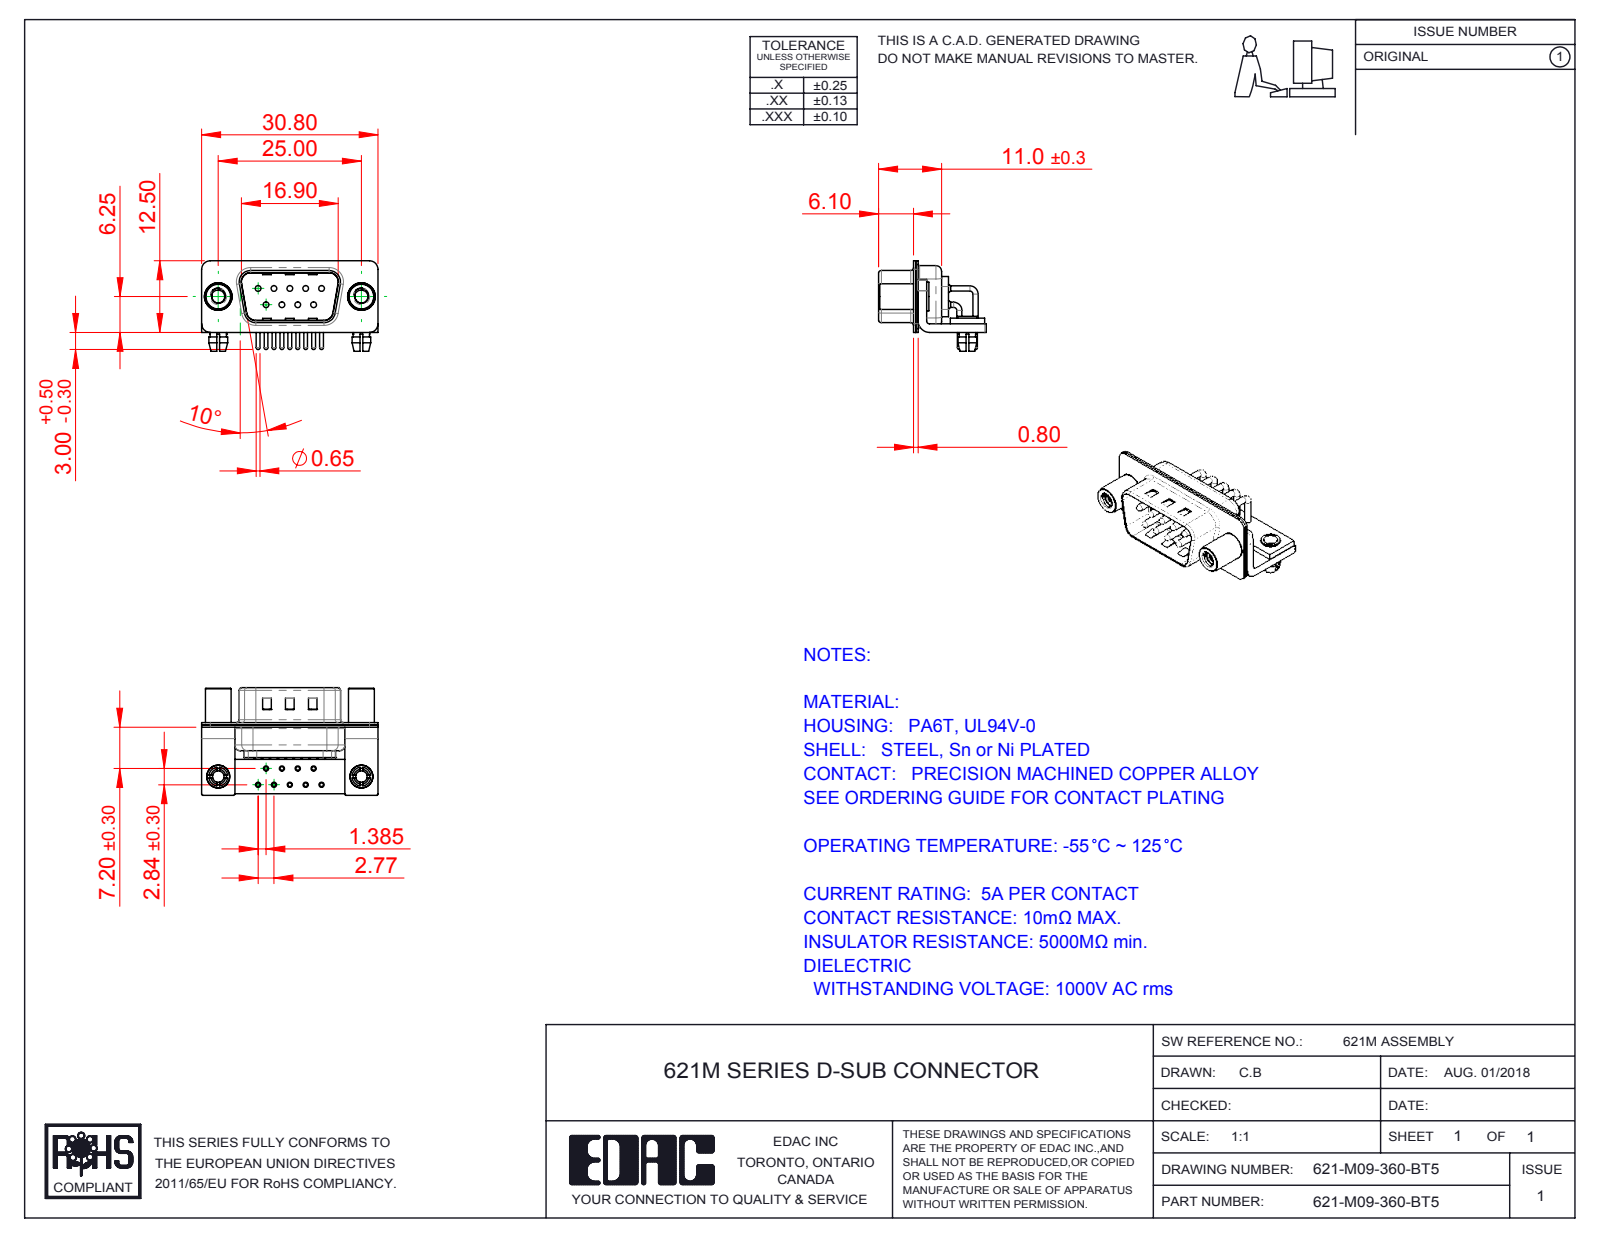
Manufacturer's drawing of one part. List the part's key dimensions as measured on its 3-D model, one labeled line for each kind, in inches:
Part name (STEP PRODUCT): 621-M09-360-BT5; 621M Contact Row 2; 621M Contact Row 1; 621M Board Lock (+6 more)
STEP written by: SolidWorks 2016 (CONFIG_CONTROL_DESIGN)
Units: inches
Bodies: 19 solids, 1504 faces (759 planar, 567 cylindrical, 178 other)
Overall size (bounding box): 1.213 × 0.74 × 0.622
Volume: 0.118 in³ · Surface area: 8.333 in²
Round holes (diameter × count): ⌀0.079 ×11, ⌀0.035 ×9, ⌀0.039 ×9, ⌀0.067 ×9, ⌀0.089 ×2, ⌀0.098 ×2, ⌀0.126 ×2, ⌀0.157 ×2, ⌀0.189 ×2
Round bosses / shafts (diameter × count): ⌀0.059 ×9, ⌀0.035 ×9, ⌀0.026 ×9, ⌀0.197 ×2, ⌀0.193 ×2, ⌀0.177 ×2, ⌀0.157 ×2, ⌀0.134 ×2
Partial cylindrical surfaces — rounded edges, fillets, slot ends (radius × count): R0.01 ×16, R0.059 ×16, R0.079 ×13, R0.02 ×9, R0.04 ×9, R0.063 ×8, R0.024 ×4, R0.026 ×4
Main face-to-face distances: 0.016, 0.059, 0.031, 0.033, 0.049, 0.075, 0.039, 0.409, 0.376, 0.098
Hole centre spacings: 0.124, 0.109, 0.218, 0.198, 0.198, 0.327, 0.294, 0.295
